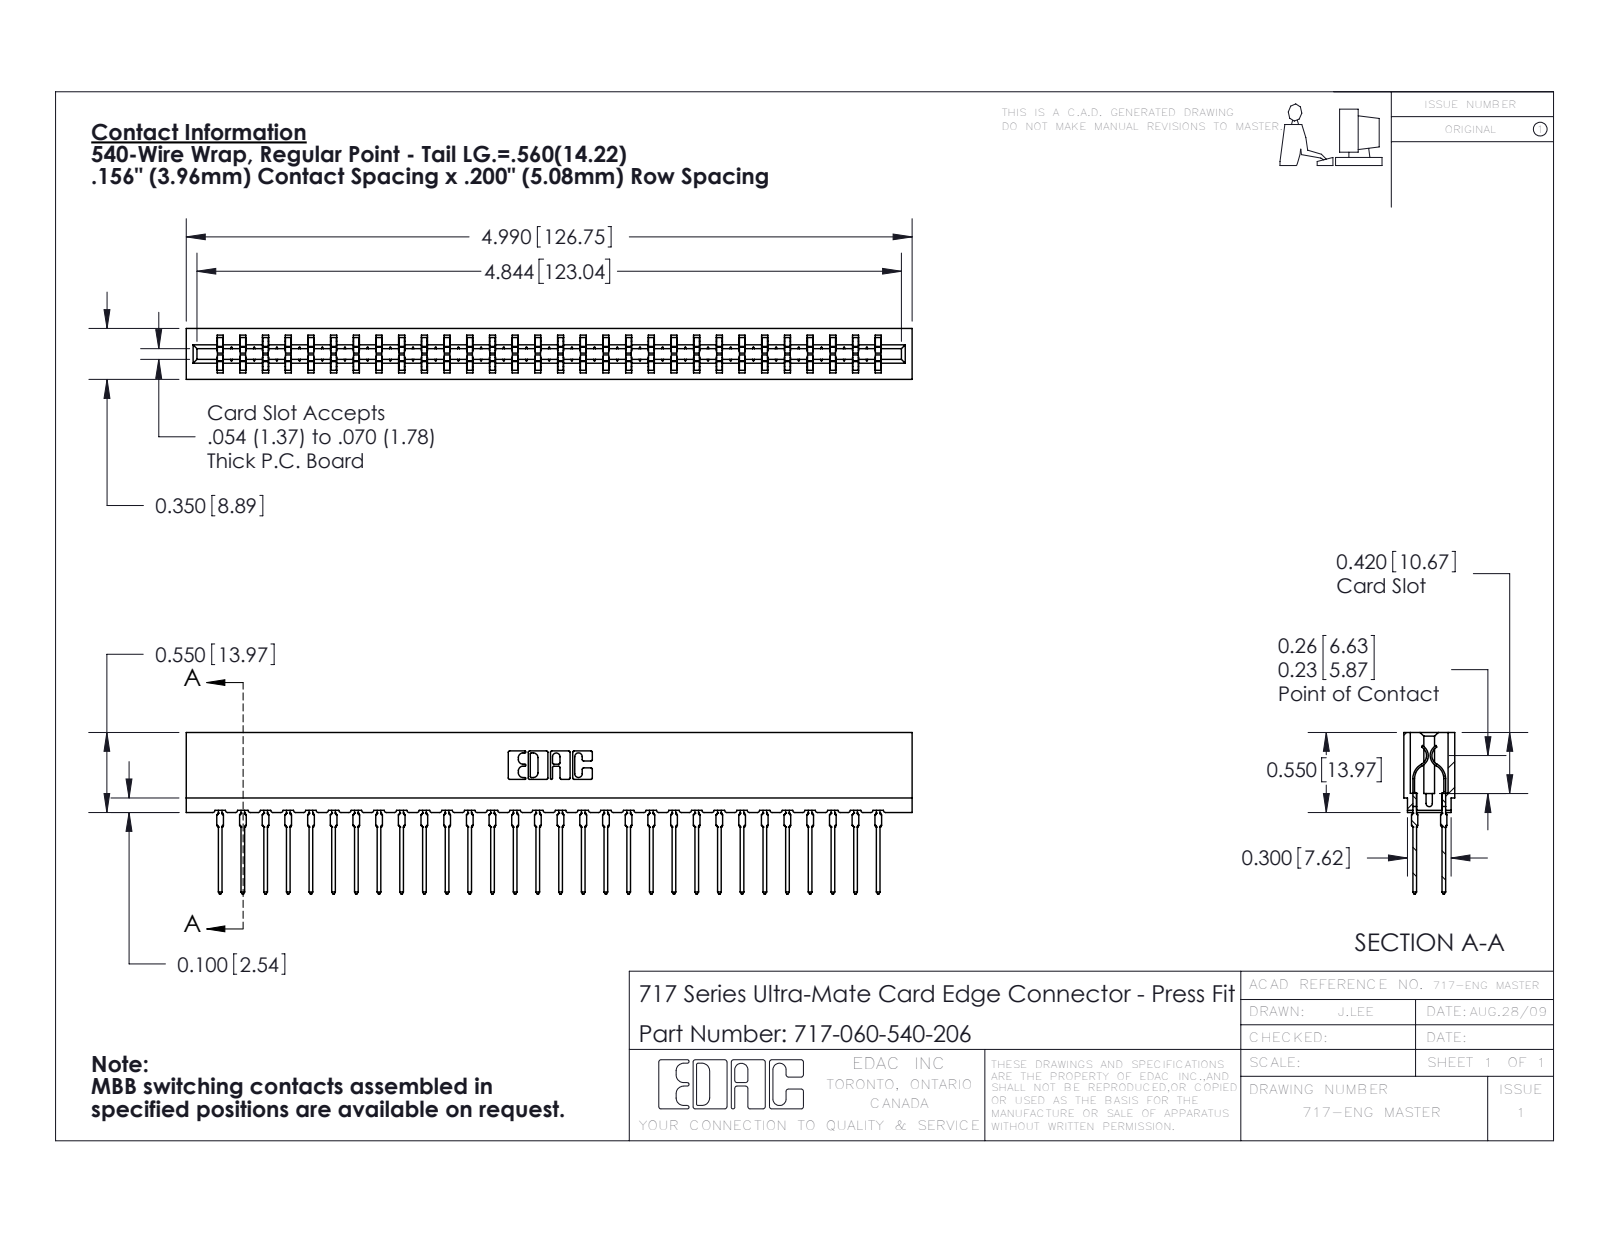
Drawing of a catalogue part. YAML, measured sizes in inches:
part_name: "717-060-540-206; 717 Part_Insulator Option - 06; 745-292-001_540"
step_written_by: "SolidWorks 2016 (CONFIG_CONTROL_DESIGN)"
units: inches
bodies: {solids: 61, faces: 5494, planar: 2844, cylindrical: 1090, other: 1560}
overall_size: [4.99, 1.109, 0.35]
volume: 0.684
surface_area: 27.54
partial_cylinders:
  - {radius: 0.021, count: 120}
  - {radius: 0.015, count: 60}
  - {radius: 0.01, count: 22}
  - {radius: 0.005, count: 8}
  - {radius: 0.011, count: 8}
  - {radius: 0.007, count: 6}
  - {radius: 0.031, count: 6}
  - {radius: 0.026, count: 3}
face_to_face_distances: [0.212, 0.138, 0.35, 0.063, 0.287, 0.076, 0.149, 0.074, 0.156, 0.087]
